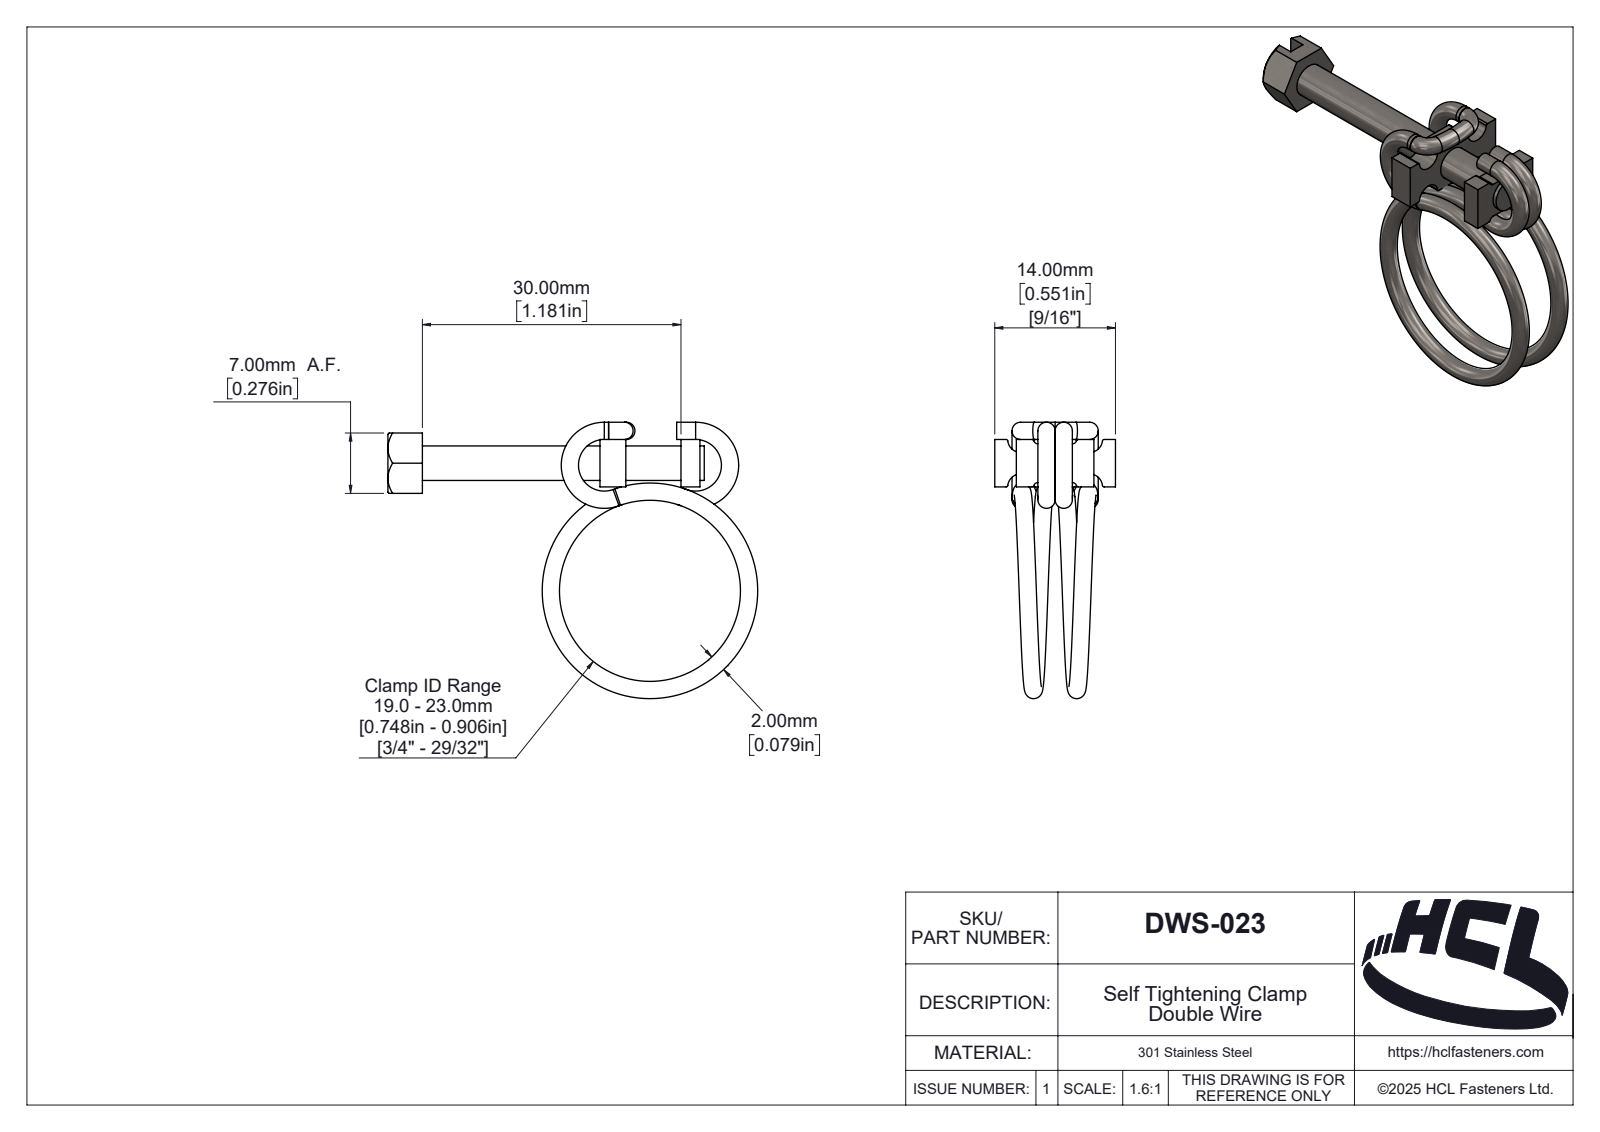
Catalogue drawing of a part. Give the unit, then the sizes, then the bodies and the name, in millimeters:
Units: millimetres
Overall size (bounding box): 42.9 × 32.05 × 14
Round holes (diameter × count): ⌀4 ×1
Round bosses / shafts (diameter × count): ⌀2 ×4
Partial cylindrical surfaces — rounded edges, fillets, slot ends (radius × count): R0.2 ×12, R0.5 ×4, R1.5 ×4, R0.4 ×1, R0.51 ×1, R0.53 ×1, R0.64 ×1, R0.91 ×1
Main face-to-face distances: 2, 5.5, 3, 23.6, 7, 0.5, 11.6, 8.6, 9.4, 6.4
Volume: 1 502 mm³ · Surface area: 2 518 mm²
Bodies: 6 solids, 213 faces (53 planar, 74 cylindrical, 86 other)
Part name (STEP PRODUCT): DWS-023
STEP written by: SolidWorks 2025 (AUTOMOTIVE_DESIGN)
